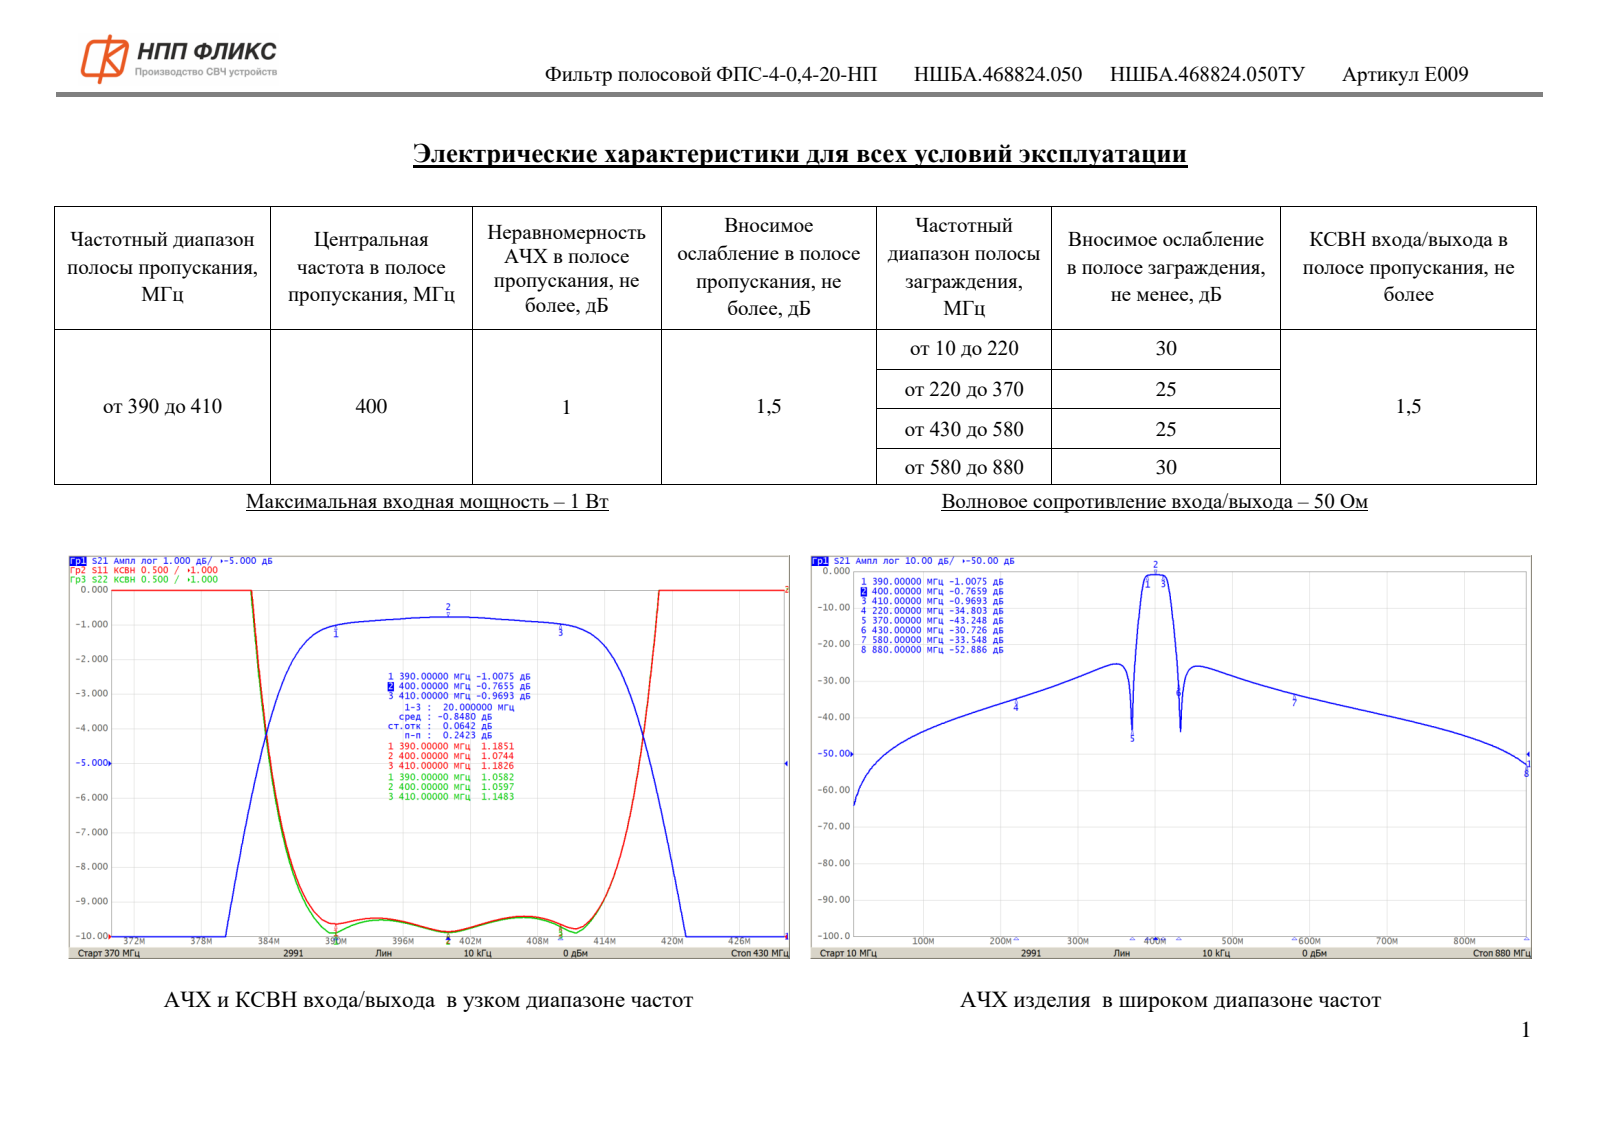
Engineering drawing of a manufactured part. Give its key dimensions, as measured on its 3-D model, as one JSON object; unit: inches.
{"part_name": "НШБА.468824.050_Фильтр ФПС-4-0,4-20-НП", "step_written_by": "ASCON Math Kernel (CONFIG_CONTROL_DESIGN)", "units": "inches", "bodies": {"solids": 3, "faces": 700, "planar": 513, "cylindrical": 79, "other": 108}, "overall_size": [0.984, 0.669, 0.351], "volume_in3": 0.039, "surface_area_in2": 4.666, "round_holes": [[0.028, 4], [0.02, 2]], "partial_cylinders_radius": [[0.016, 18], [0.012, 8], [0.018, 8], [0.024, 8], [0.039, 8], [0.02, 3], [0.01, 1], [0.03, 1]], "face_to_face_distances": [0.032, 0.339, 0.307, 0.602, 0.319, 0.351, 0.917, 0.591, 0.614, 0.906], "hole_center_spacings": [0.395, 0.716, 0.394, 0.602, 0.72, 0.906]}
